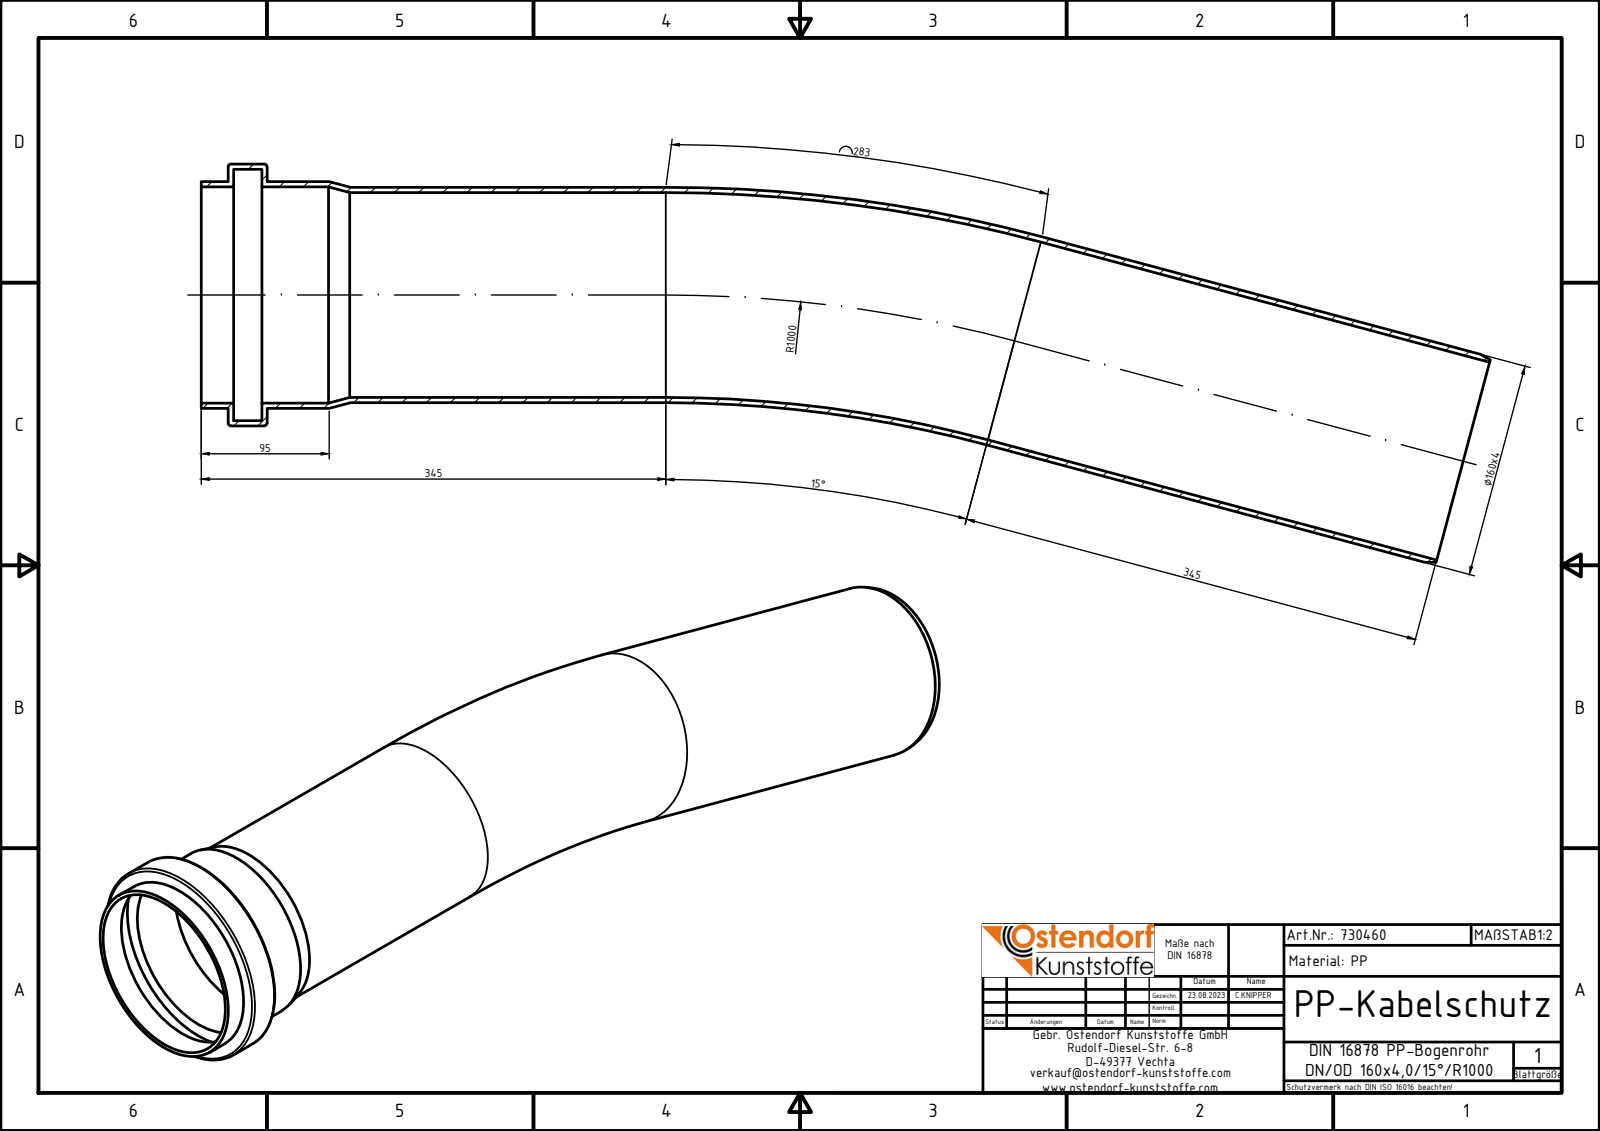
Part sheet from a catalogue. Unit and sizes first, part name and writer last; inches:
Units: inches
Overall size (bounding box): 37.685 × 11.646 × 7.657
Round holes (diameter × count): ⌀5.984 ×2, ⌀6.319 ×1, ⌀7.343 ×1
Round bosses / shafts (diameter × count): ⌀6.299 ×2, ⌀7.657 ×1, ⌀6.634 ×1
Main face-to-face distances: 0.157, 0.984, 0.827, 1.142, 0.787, 0.945, 1.772, 1.929
Volume: 118.3 in³ · Surface area: 1 510 in²
Bodies: 1 solid, 23 faces (6 planar, 10 cylindrical, 7 other)
Part name (STEP PRODUCT): PP-Bogenrohr_160x40_R1000_15_SM_34865_730460
STEP written by: Autodesk Inventor 2024 (AUTOMOTIVE_DESIGN)
